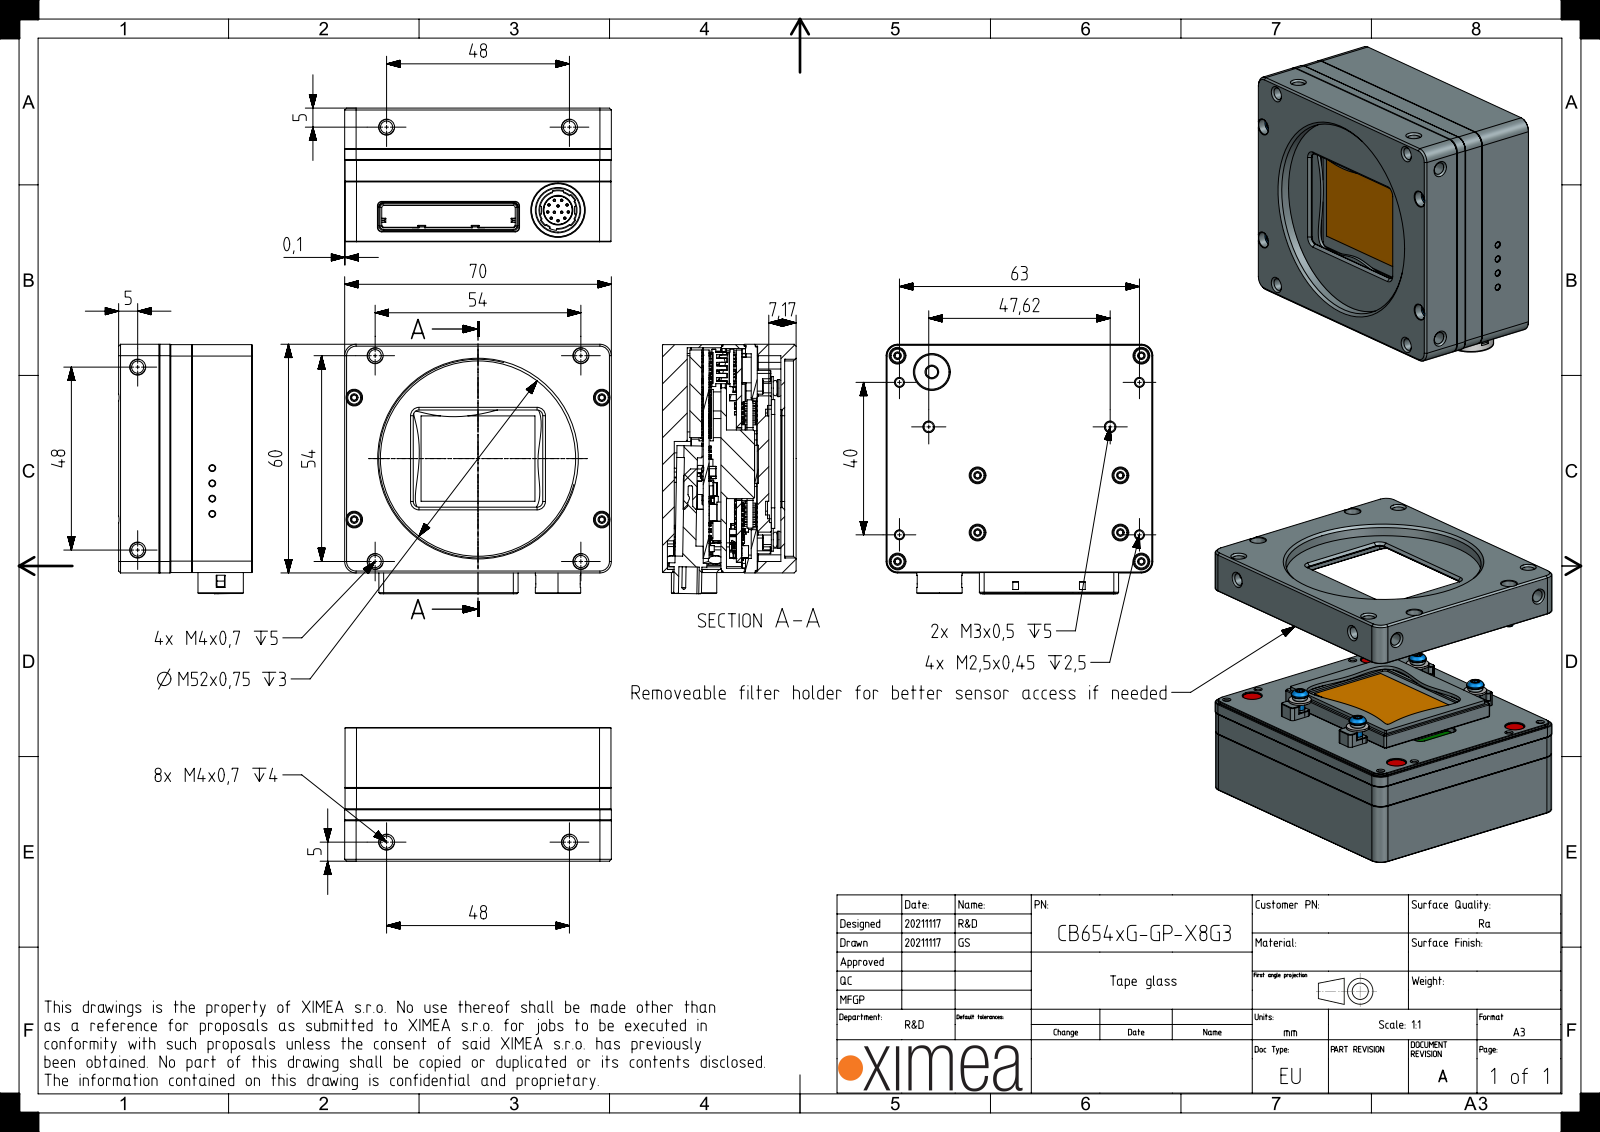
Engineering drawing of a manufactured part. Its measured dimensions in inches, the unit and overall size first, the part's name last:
Units: inches
Overall size (bounding box): 2.756 × 2.578 × 1.381
Round holes (diameter × count): ⌀0.031 ×239, ⌀0.083 ×26, ⌀0.026 ×24, ⌀0.022 ×23, ⌀0.079 ×22, ⌀0.051 ×18, ⌀0.063 ×18, ⌀0.039 ×14, ⌀0.024 ×13, ⌀0.047 ×12, ⌀0.161 ×12, ⌀0.03 ×9
Round bosses / shafts (diameter × count): ⌀0.038 ×239, ⌀0.012 ×239, ⌀0.15 ×14, ⌀0.043 ×12, ⌀0.035 ×12, ⌀0.022 ×12, ⌀0.021 ×12, ⌀0.042 ×9
Partial cylindrical surfaces — rounded edges, fillets, slot ends (radius × count): R0.011 ×100, R0.015 ×54, R0.004 ×50, R0.006 ×50, R0.118 ×45, R0.031 ×32, R0.039 ×31, R0.012 ×26
Main face-to-face distances: 0.562, 0.398, 0.157, 0.98, 0.421, 0.558, 0.256, 0.24, 0.482, 0.061
Hole centre spacings: 0.05, 0.071, 0.112, 0.1, 0.158, 0.15, 0.2, 0.206
Volume: 5.177 in³ · Surface area: 144.8 in²
Bodies: 107 solids, 35764 faces (29150 planar, 5845 cylindrical, 769 other)
Part name (STEP PRODUCT): 60-30-1112-nut; MECH-LIGHTPIPE-1.63X4.14; CB-X8G3-MAIN-PCA-LW; CB-X8G3-CONN-PCA (+8 more)
STEP written by: SIEMENS PLM Software NX 1907 (AUTOMOTIVE_DESIGN)
